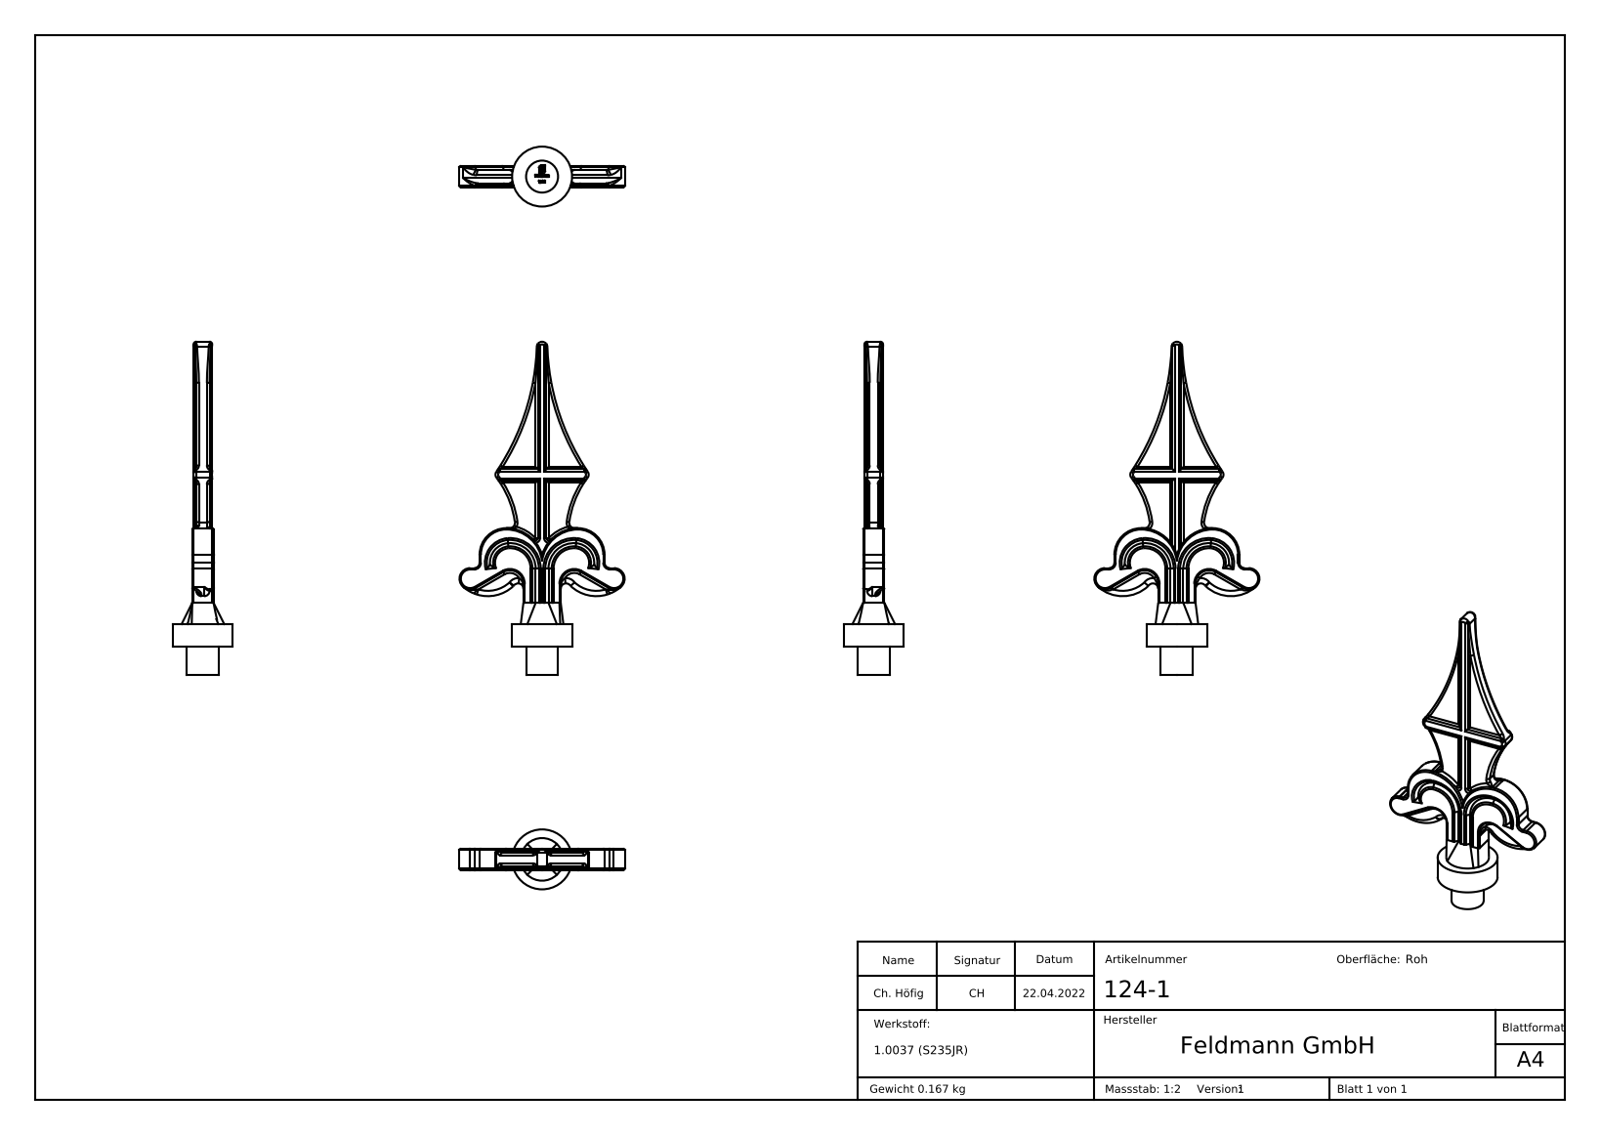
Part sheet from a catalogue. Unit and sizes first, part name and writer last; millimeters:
Units: millimetres
Overall size (bounding box): 125 × 62 × 22.5
Round bosses / shafts (diameter × count): ⌀22.5 ×1, ⌀12 ×1
Partial cylindrical surfaces — rounded edges, fillets, slot ends (radius × count): R1 ×30, R0.5 ×15, R2 ×10, R4 ×2, R5.08 ×2, R10 ×2, R14.01 ×2, R14.05 ×2
Main face-to-face distances: 1.5, 6.5, 5, 8, 1, 0.5, 7.5, 6, 7, 8.5
Volume: 21 376 mm³ · Surface area: 8 949 mm²
Bodies: 1 solid, 496 faces (174 planar, 89 cylindrical, 233 other)
Part name (STEP PRODUCT): 124-1
STEP written by: SolidWorks 2018 (CONFIG_CONTROL_DESIGN)
